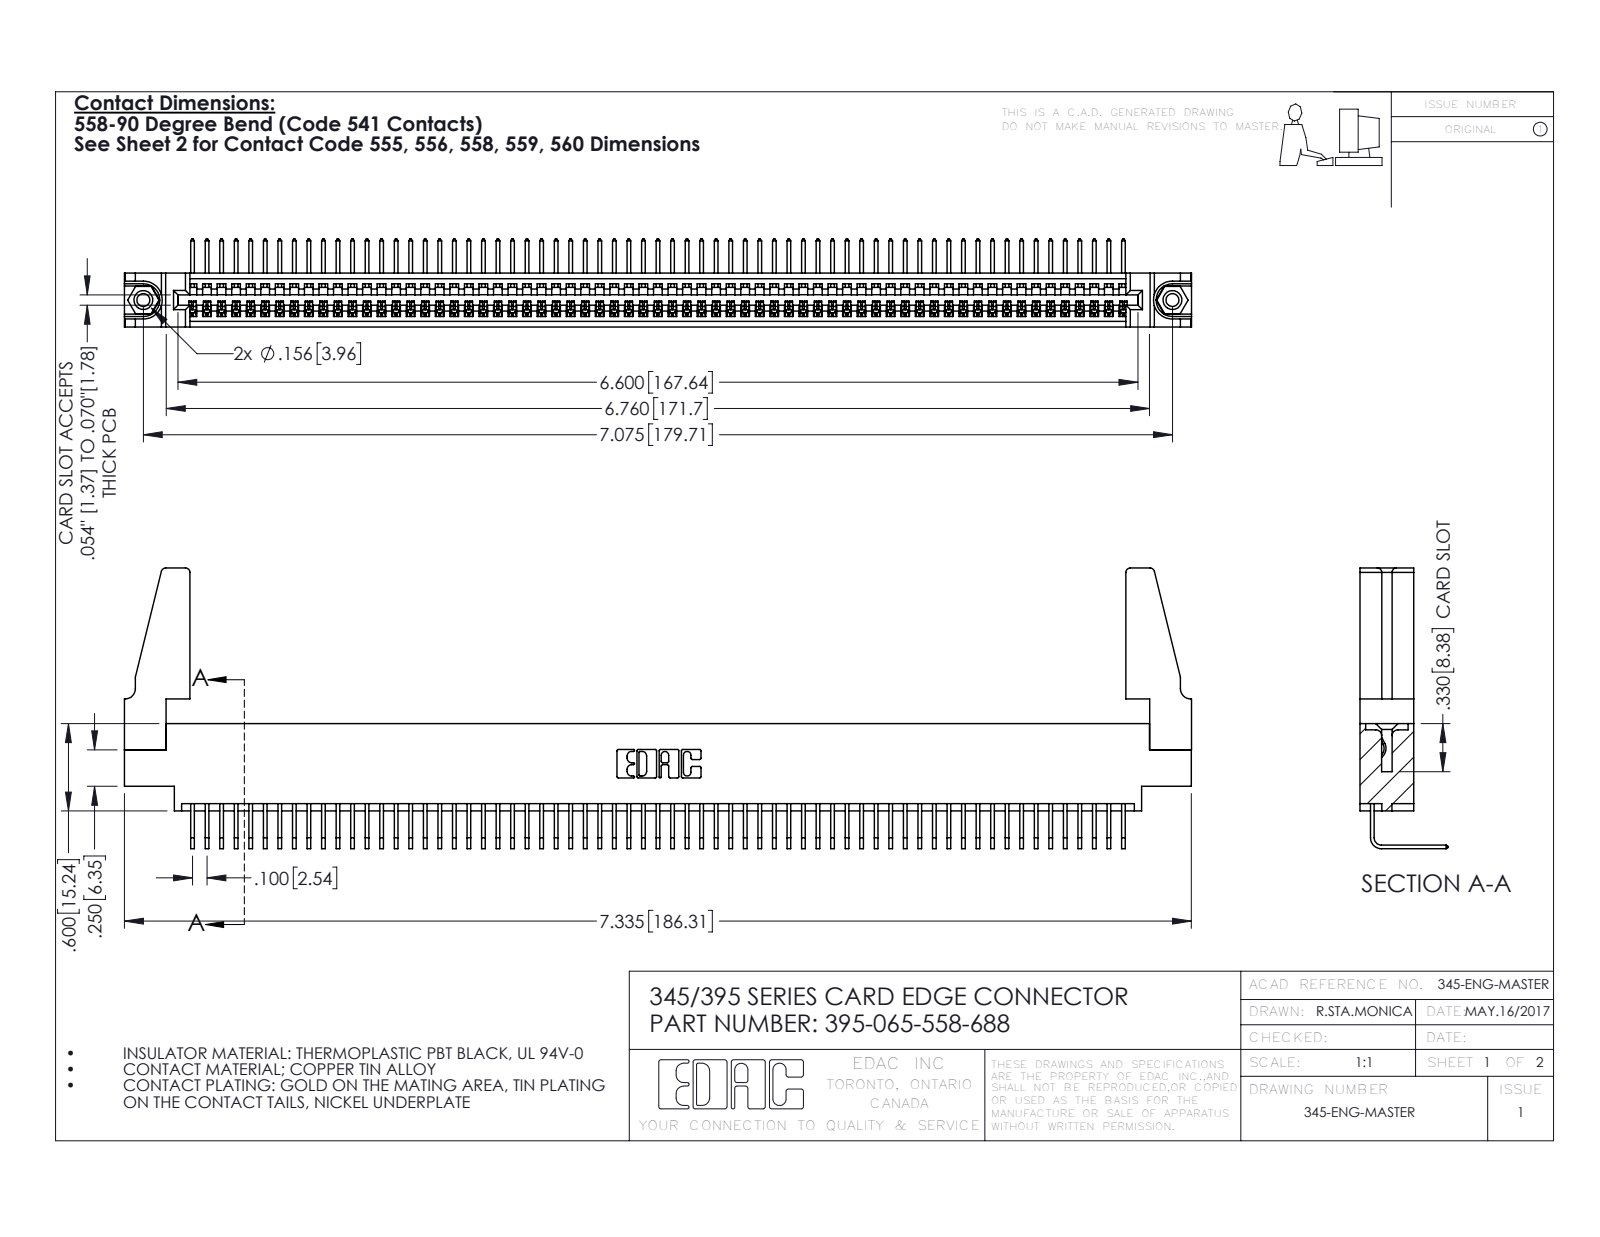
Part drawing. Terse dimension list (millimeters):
name: 395-065-558-688; 345 Part_0.170 Offset - 0.156 Dia-TH; 345-292-001_558 Tail - 2; 345-250-001_345-250-001-102 (+1 more)
written by: SolidWorks 2016 (CONFIG_CONTROL_DESIGN)
unit: mm
bodies: 70 solids, 4154 faces (2886 planar, 1252 cylindrical, 16 other)
size: 186.3 × 49 × 15.4
volume: 21 240 mm³; area: 28 750 mm²
holes: 2× ⌀2.3, 2× ⌀3.2, 2× ⌀4, 1× ⌀1.6
bosses: 2× ⌀3.9
rounds: 130× R0.2, 22× R0.3, 8× R0.8, 6× R0.2, 6× R0.8, 3× R0.7, 2× R0.8, 2× R1
face distances: 1.8, 7.6, 9.4, 5.1, 2.5, 6.9, 0.6, 5.7, 4.4, 3.8
hole spacings: 6.9, 173.7, 179.7
